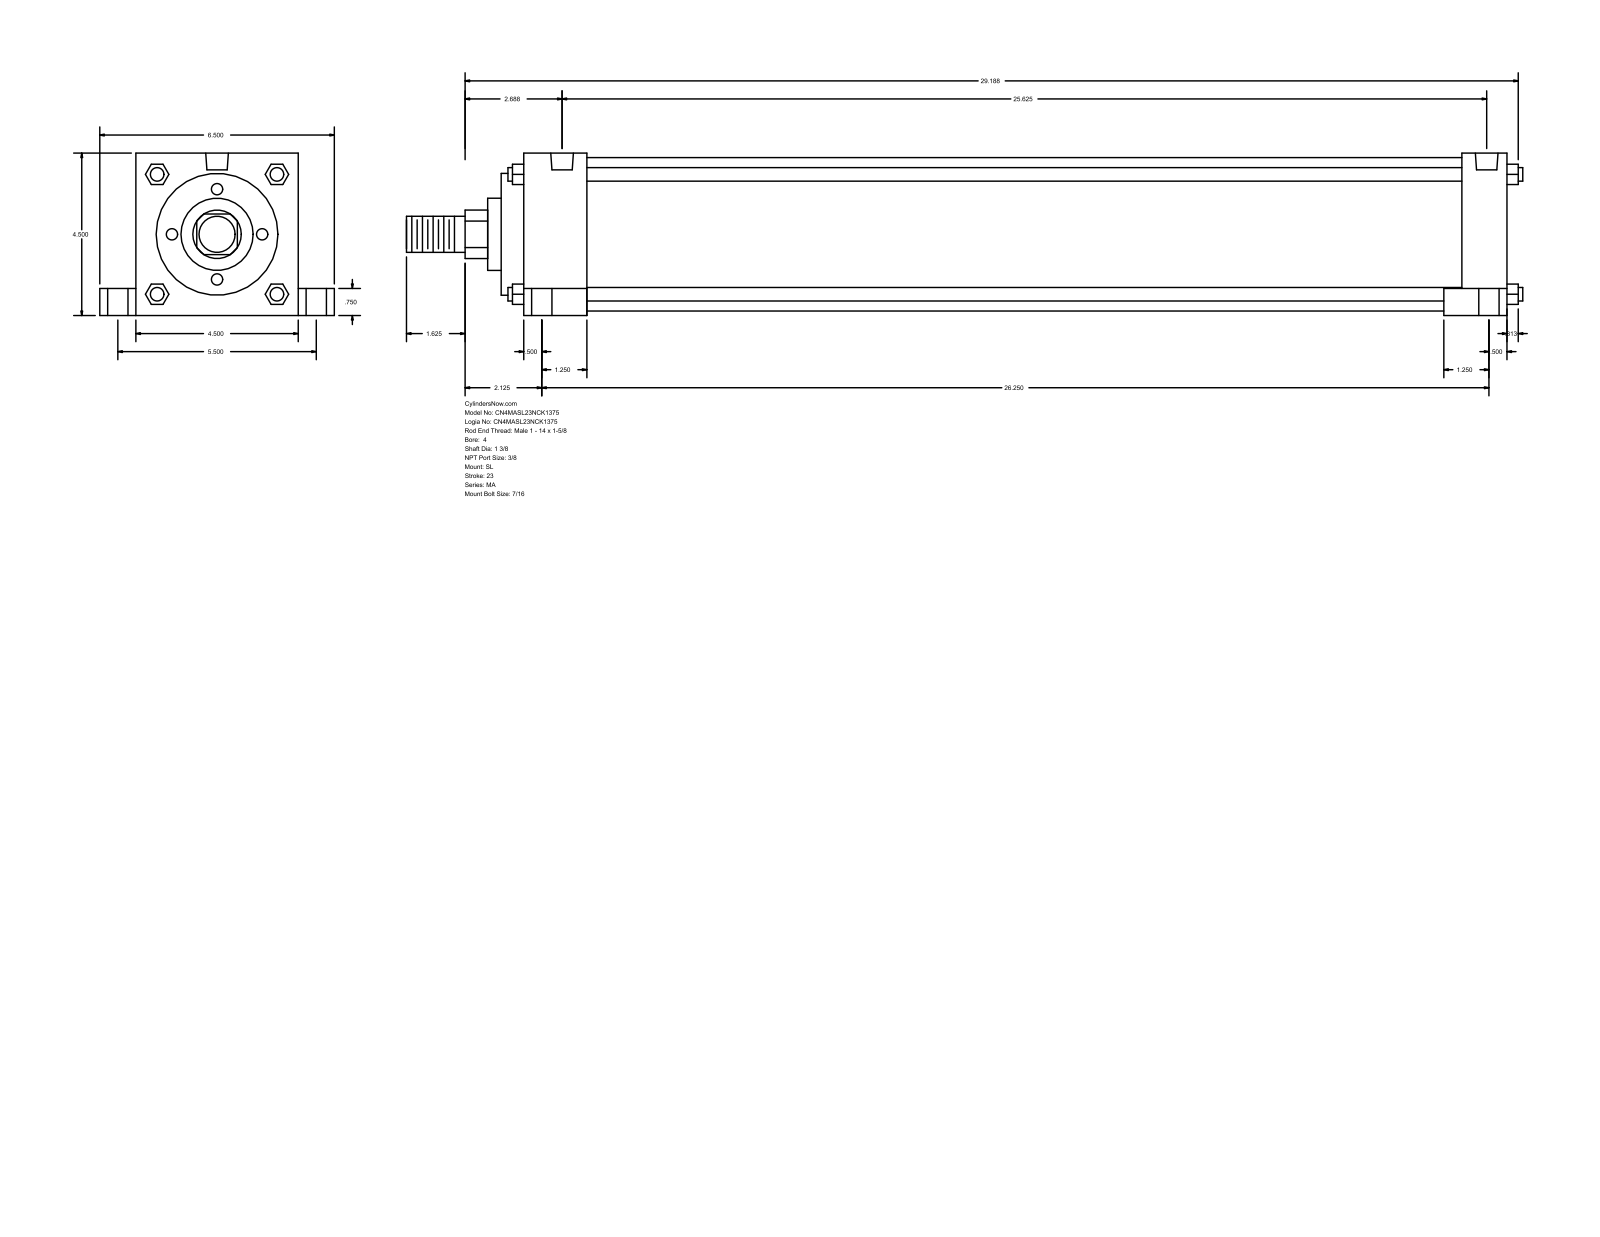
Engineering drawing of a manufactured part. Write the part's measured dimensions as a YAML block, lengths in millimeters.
part_name: "MA_SL__0400_1.375"
step_written_by: "GSSL Pune (CONFIG_CONTROL_DESIGN)"
units: millimeters
bodies: {solids: 0, faces: 150, planar: 113, cylindrical: 37, other: 0}
overall_size: [785.81, 165.1, 114.3]
round_holes:
  - {diameter: 11.11, count: 4}
  - {diameter: 14.29, count: 4}
  - {diameter: 20.64, count: 4}
  - {diameter: 15.93, count: 2}
round_bosses_or_shafts:
  - {diameter: 9.53, count: 4}
  - {diameter: 107.95, count: 1}
  - {diameter: 85.72, count: 1}
  - {diameter: 50.8, count: 1}
  - {diameter: 34.92, count: 1}
  - {diameter: 25.4, count: 1}
partial_cylinders:
  - {radius: 17.06, count: 1}
face_to_face_distances: [114.3, 692.15, 615.95, 708.02, 15.87, 60.32, 44.45, 647.7, 676.27, 660.4]
hole_center_spacings: [69.87, 70.14, 71.29, 72.4, 139.7, 641.35, 651.46, 656.2]
